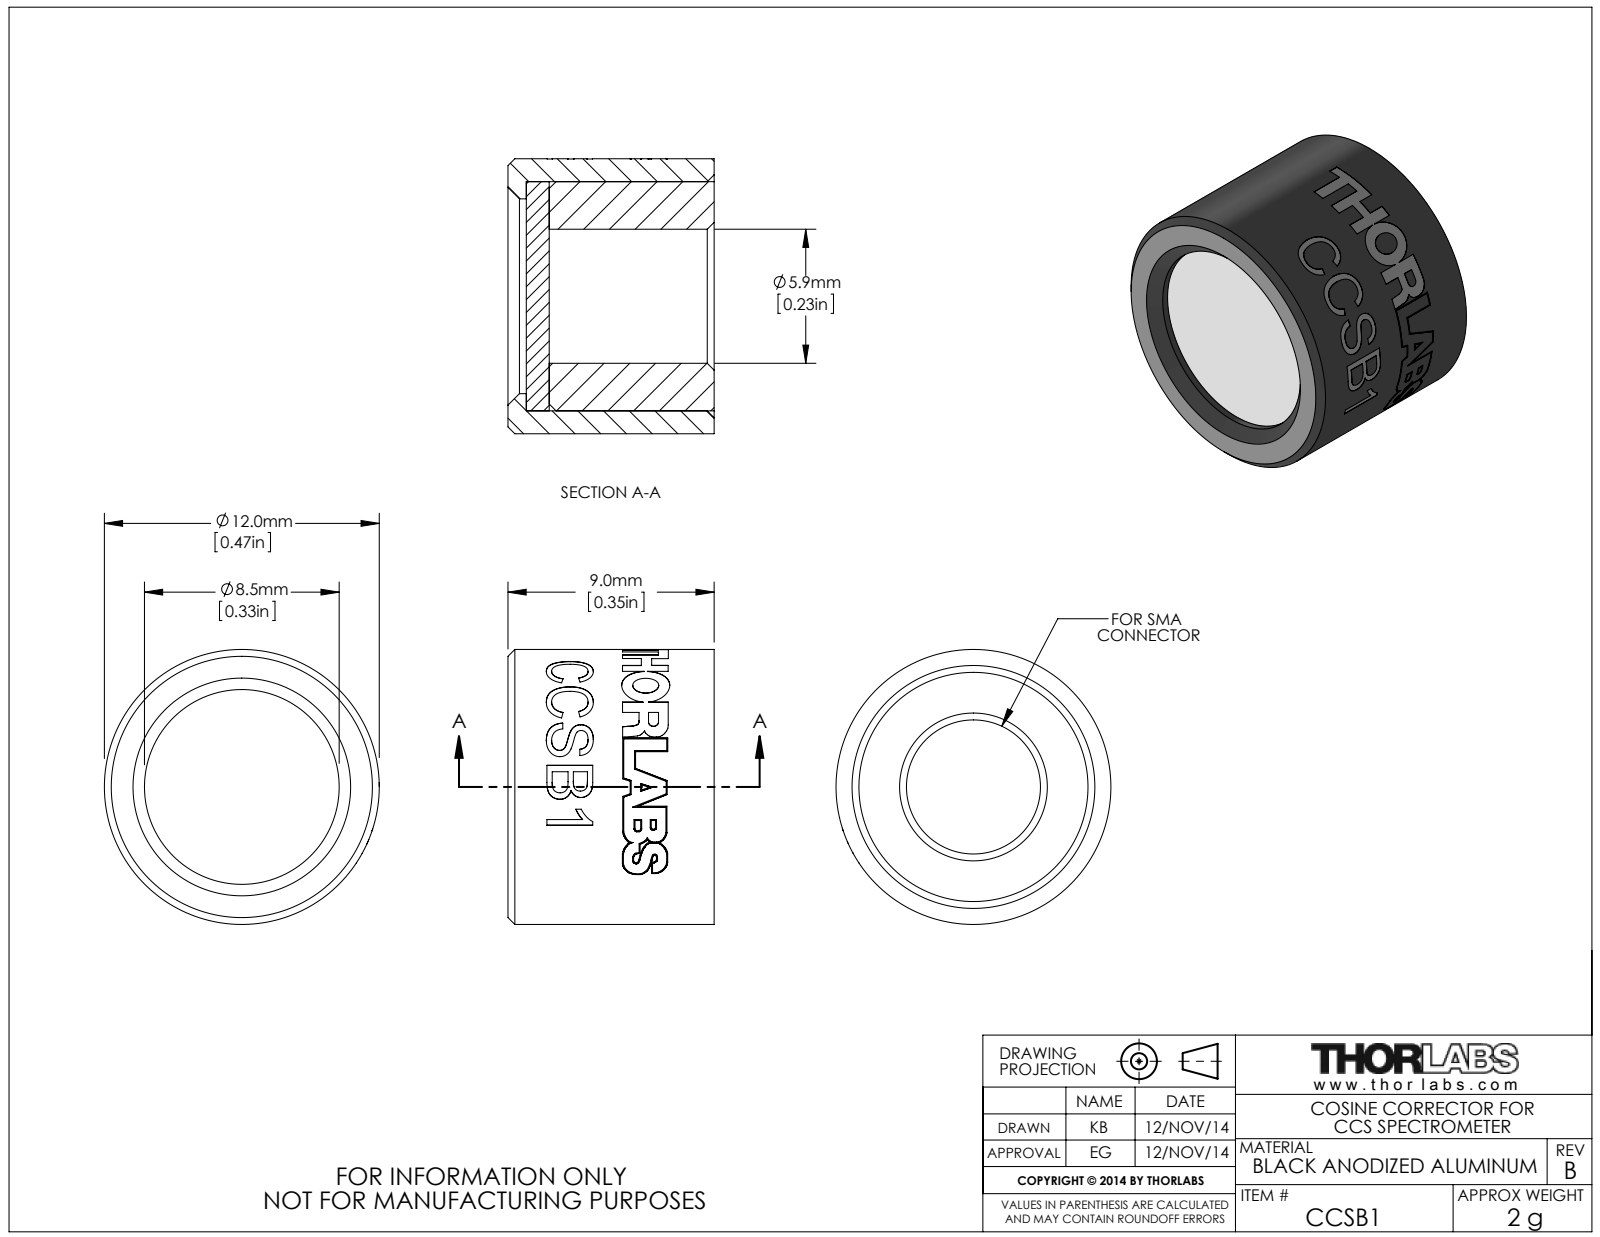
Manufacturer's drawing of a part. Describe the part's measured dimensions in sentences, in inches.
The part is named "MTN0030855-E0W-CCSB1". Its 3-D file was written by "SolidWorks 2014 (AUTOMOTIVE_DESIGN)". It is 3 solids with 464 faces: 106 planar, 25 cylindrical and 333 other. Overall it measures 0.472 by 0.472 by 0.354 inches. Its volume is 0.047 cubic inches and its surface area 2.099 square inches. Round holes: 1 of diameter 0.23, 1 of diameter 0.335. Round bosses or shafts: 1 of diameter 0.472, 1 of diameter 0.394. Partial cylindrical surfaces (rounded edges, fillets, slot ends): 1 of radius 0.236. The main face-to-face distances are 0.039, 0.323, 0.283, 0.031, 0.071, 0.354, 0.079, 0.126, 0.157, 0.076.
